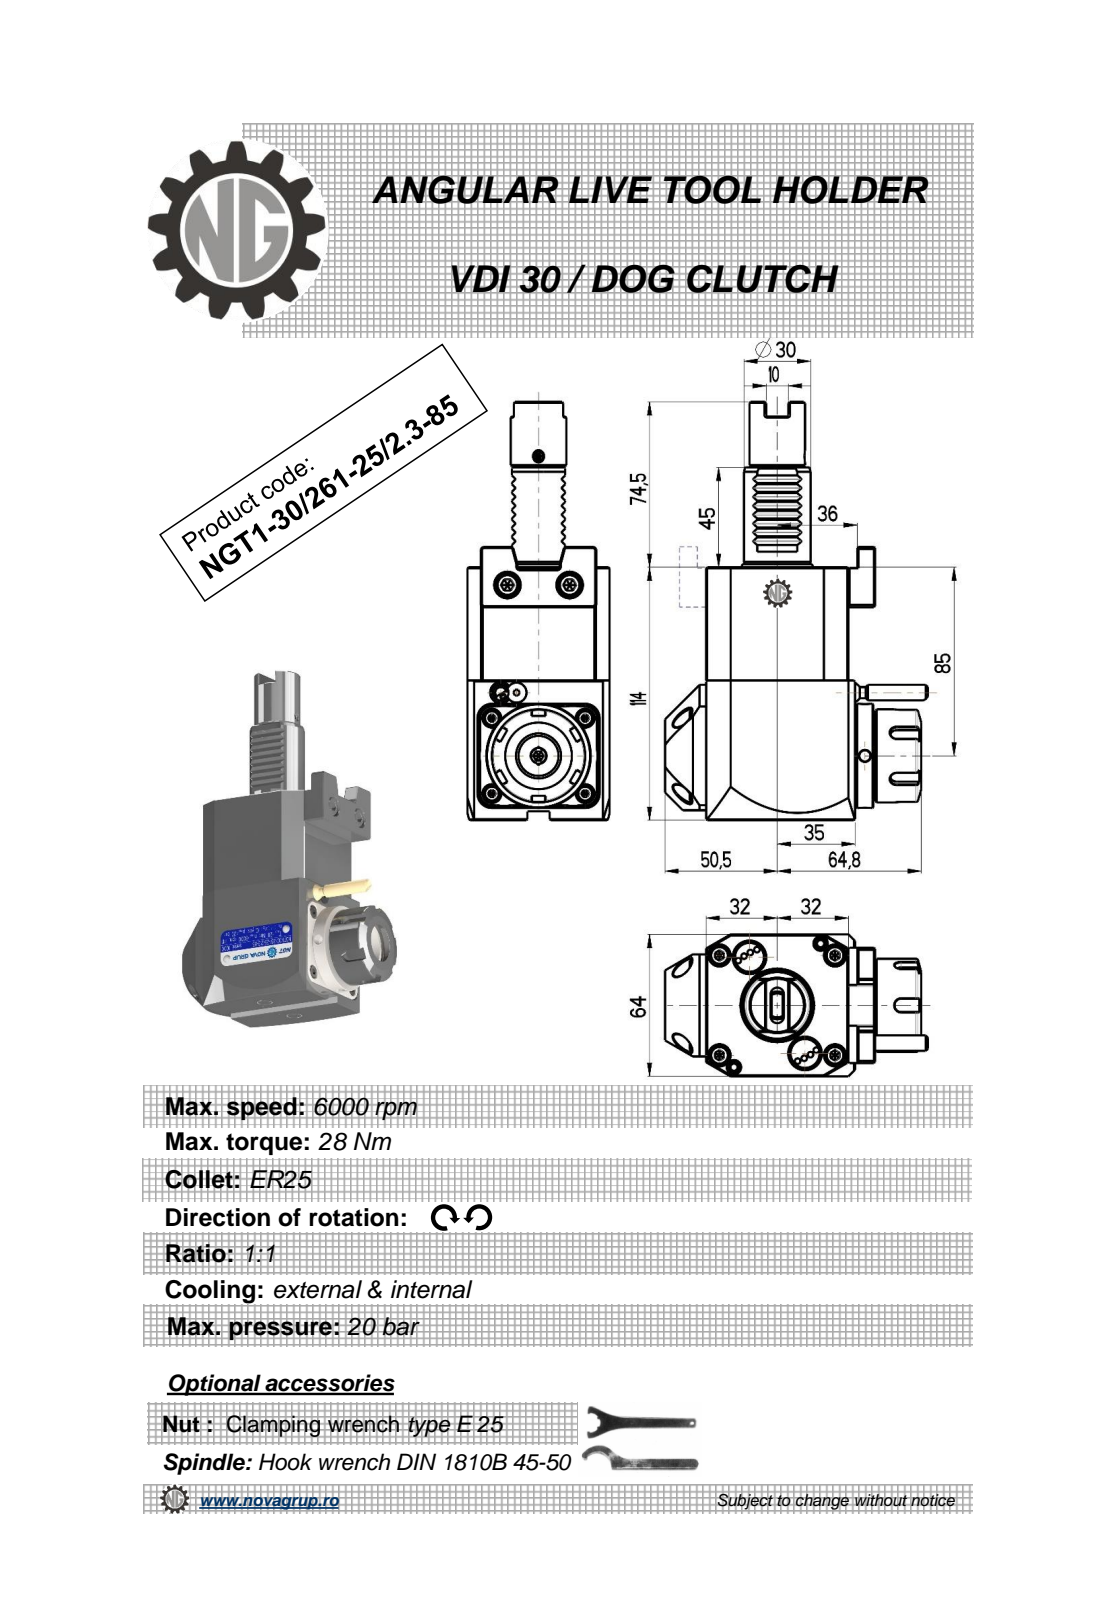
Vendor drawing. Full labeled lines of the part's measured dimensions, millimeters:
Part name (STEP PRODUCT): NGT1_30_261_25_2_3_85
STEP written by: PRO/ENGINEER BY PARAMETRIC TECHNOLOGY CORPORATION, 2010280 (CONFIG_CONTROL_DESIGN)
Units: millimetres
Bodies: 1 solid, 429 faces (225 planar, 70 cylindrical, 134 other)
Overall size (bounding box): 188.5 × 118.33 × 64
Volume: 590 931 mm³ · Surface area: 56 514 mm²
Round holes (diameter × count): ⌀5 ×2, ⌀2.5 ×1, ⌀3 ×1, ⌀4.2 ×1, ⌀20.3 ×1
Round bosses / shafts (diameter × count): ⌀47 ×1, ⌀42 ×1, ⌀35 ×1, ⌀30 ×1, ⌀25 ×1, ⌀8.96 ×1, ⌀7 ×1, ⌀5 ×1
Partial cylindrical surfaces — rounded edges, fillets, slot ends (radius × count): R0.3 ×16, R0.26 ×6, R3 ×5, R0.5 ×2, R1 ×2, R160 ×2, R32 ×1
Main face-to-face distances: 64, 114, 9, 3, 0.5, 67.2, 3.2, 76.42, 67, 0.8
Hole centre spacings: 33.19, 107.85, 135
